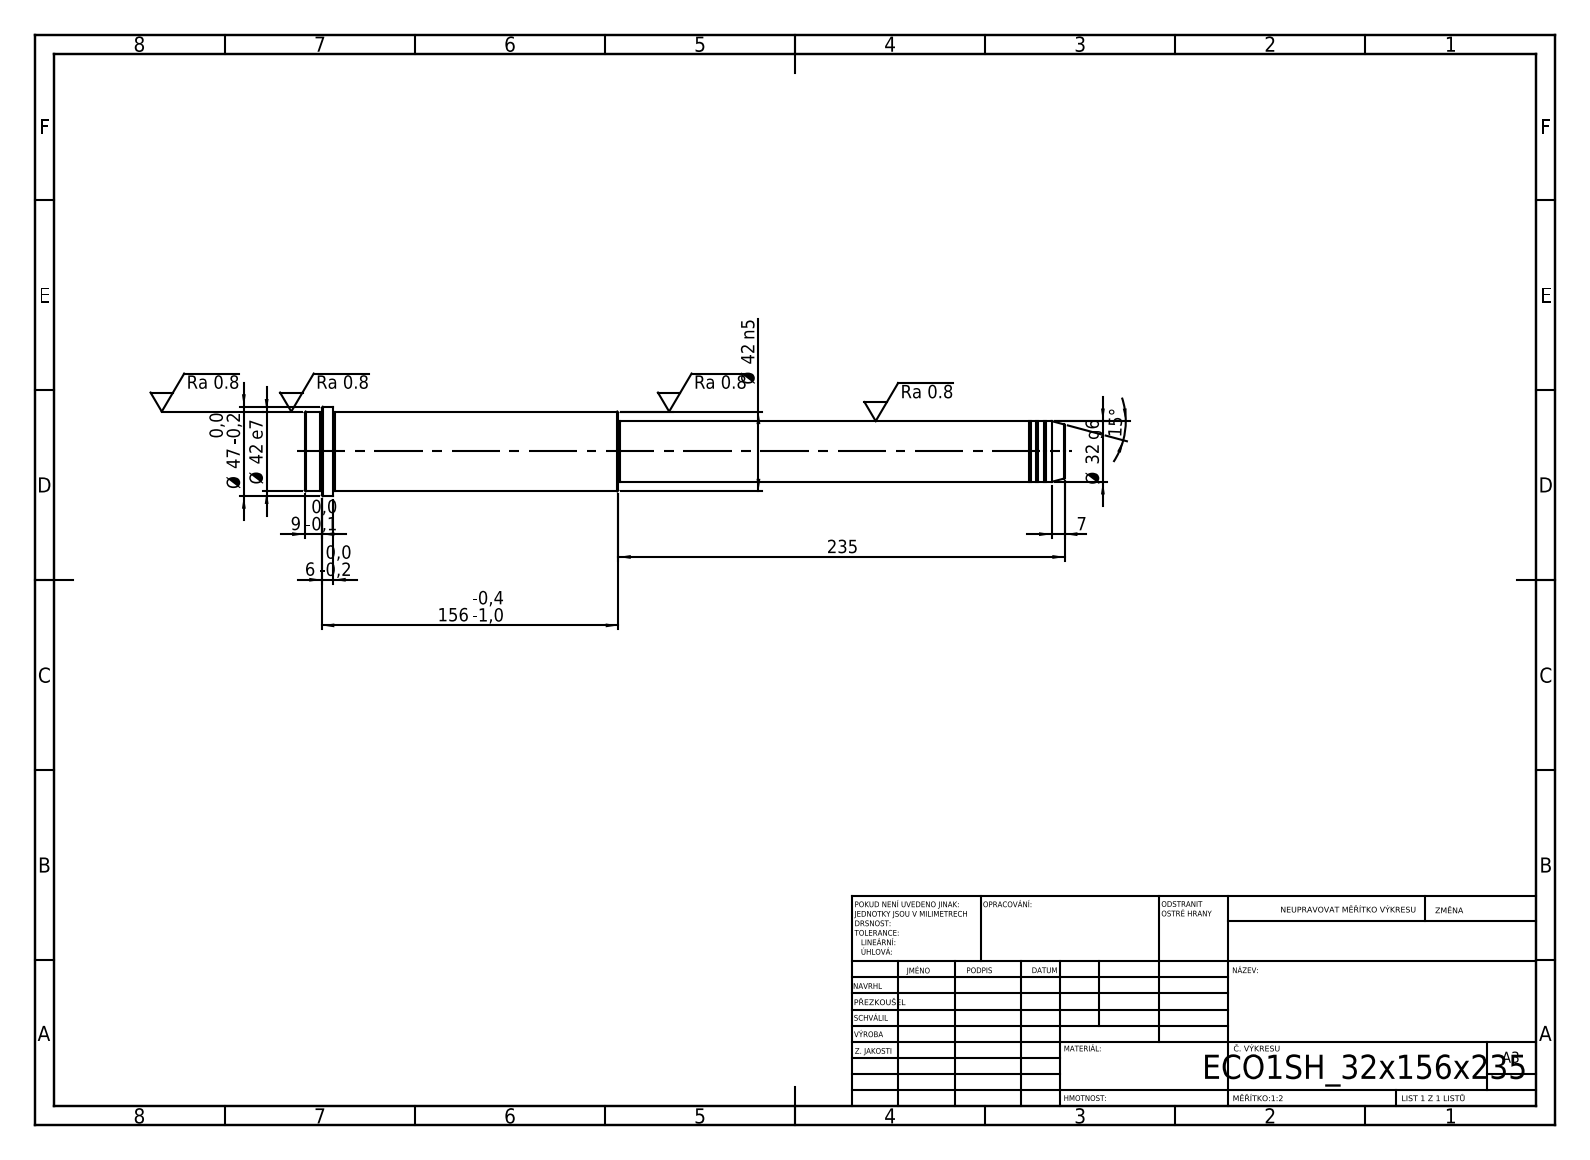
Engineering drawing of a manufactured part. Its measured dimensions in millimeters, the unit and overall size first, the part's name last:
Units: millimetres
Overall size (bounding box): 400 × 47 × 47
Round bosses / shafts (diameter × count): ⌀47 ×1, ⌀42 ×1, ⌀32 ×1, ⌀31 ×1
Main face-to-face distances: 400, 235, 165, 385, 150, 15, 391, 156, 6, 9
Volume: 418 737 mm³ · Surface area: 49 036 mm²
Bodies: 1 solid, 52 faces (6 planar, 16 cylindrical, 30 other)
STEP written by: SolidWorks 2019 (CONFIG_CONTROL_DESIGN)
